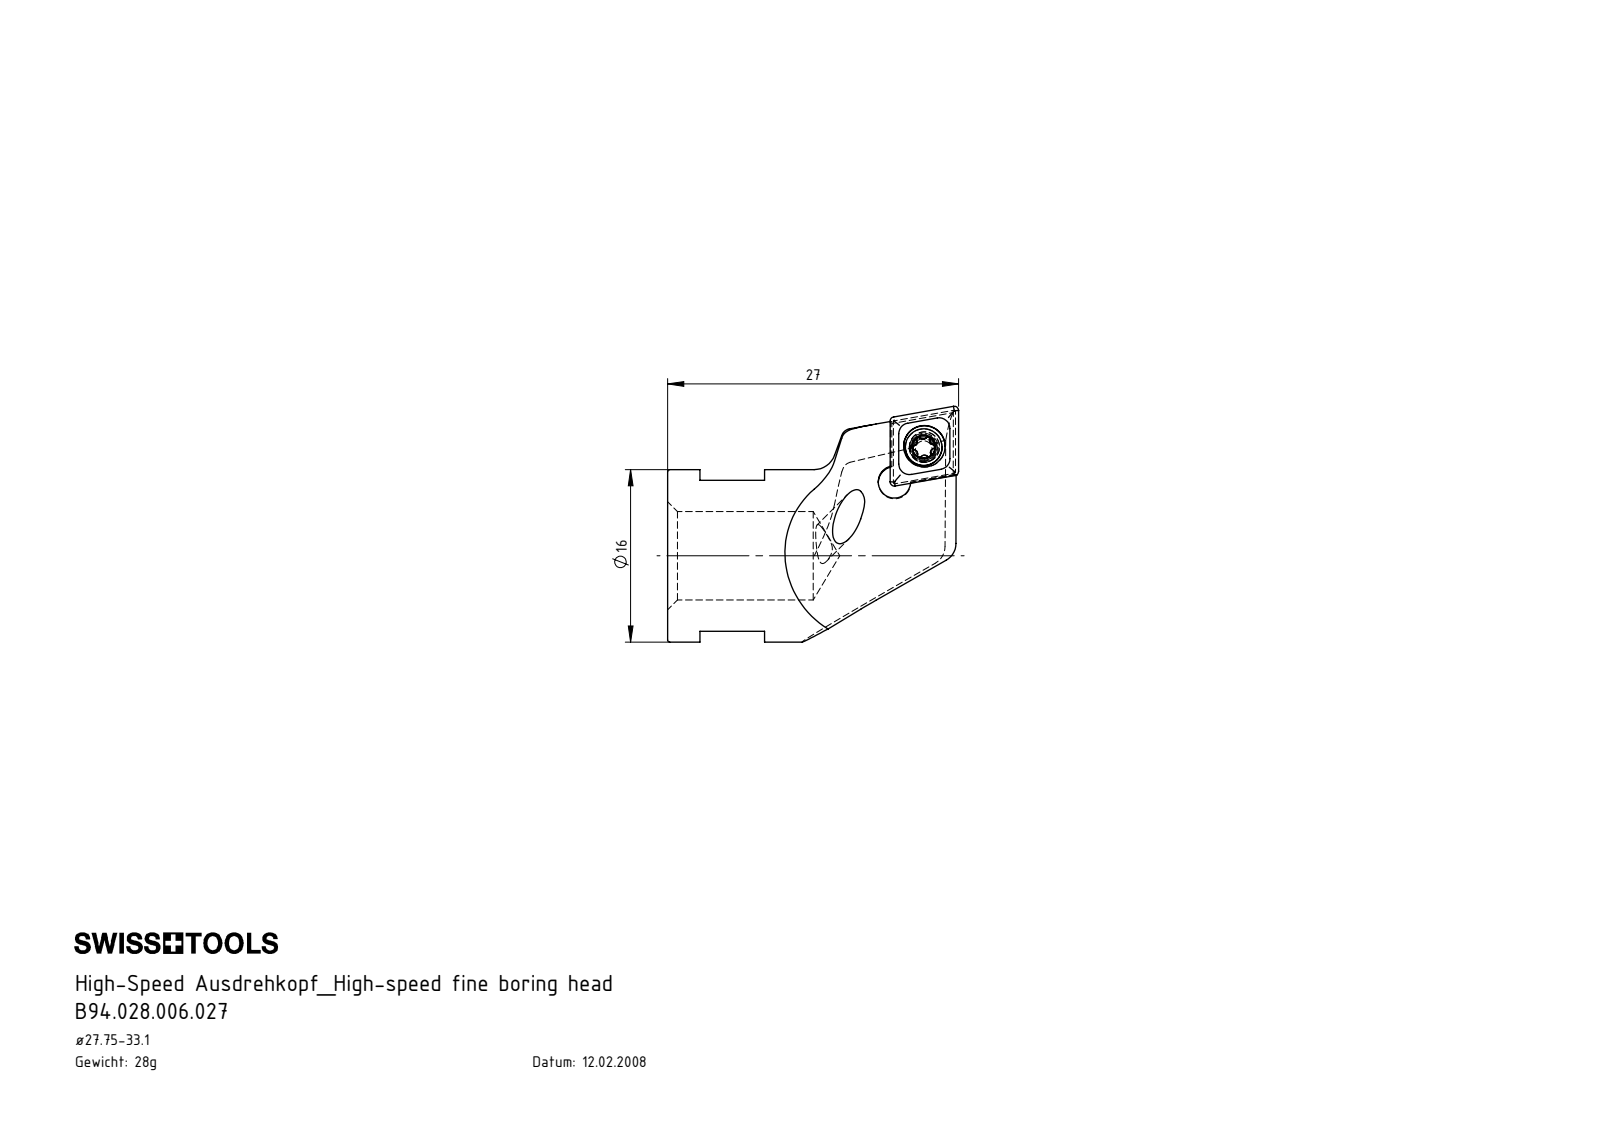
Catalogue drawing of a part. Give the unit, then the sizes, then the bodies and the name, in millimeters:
Units: millimetres
Overall size (bounding box): 27 × 21.88 × 16
Round holes (diameter × count): ⌀2.05 ×1, ⌀2.8 ×1, ⌀3 ×1, ⌀3.85 ×1, ⌀8.2 ×1
Round bosses / shafts (diameter × count): ⌀16 ×1, ⌀3.4 ×1, ⌀2.5 ×1
Partial cylindrical surfaces — rounded edges, fillets, slot ends (radius × count): R0.21 ×6, R0.36 ×4, R0.36 ×2, R1.5 ×1, R1.8 ×1, R2 ×1
Main face-to-face distances: 2.28, 1, 15, 14, 9, 3, 6, 2.38, 20.8, 17.8
Volume: 3 501 mm³ · Surface area: 2 213 mm²
Bodies: 3 solids, 97 faces (34 planar, 23 cylindrical, 40 other)
Part name (STEP PRODUCT): WCA-ER2.001.006_A; CCMT060204; HS0.A28.K11.027; HS0-A28.K11.027_C
STEP written by: SolidWorks 2017 (AUTOMOTIVE_DESIGN)
